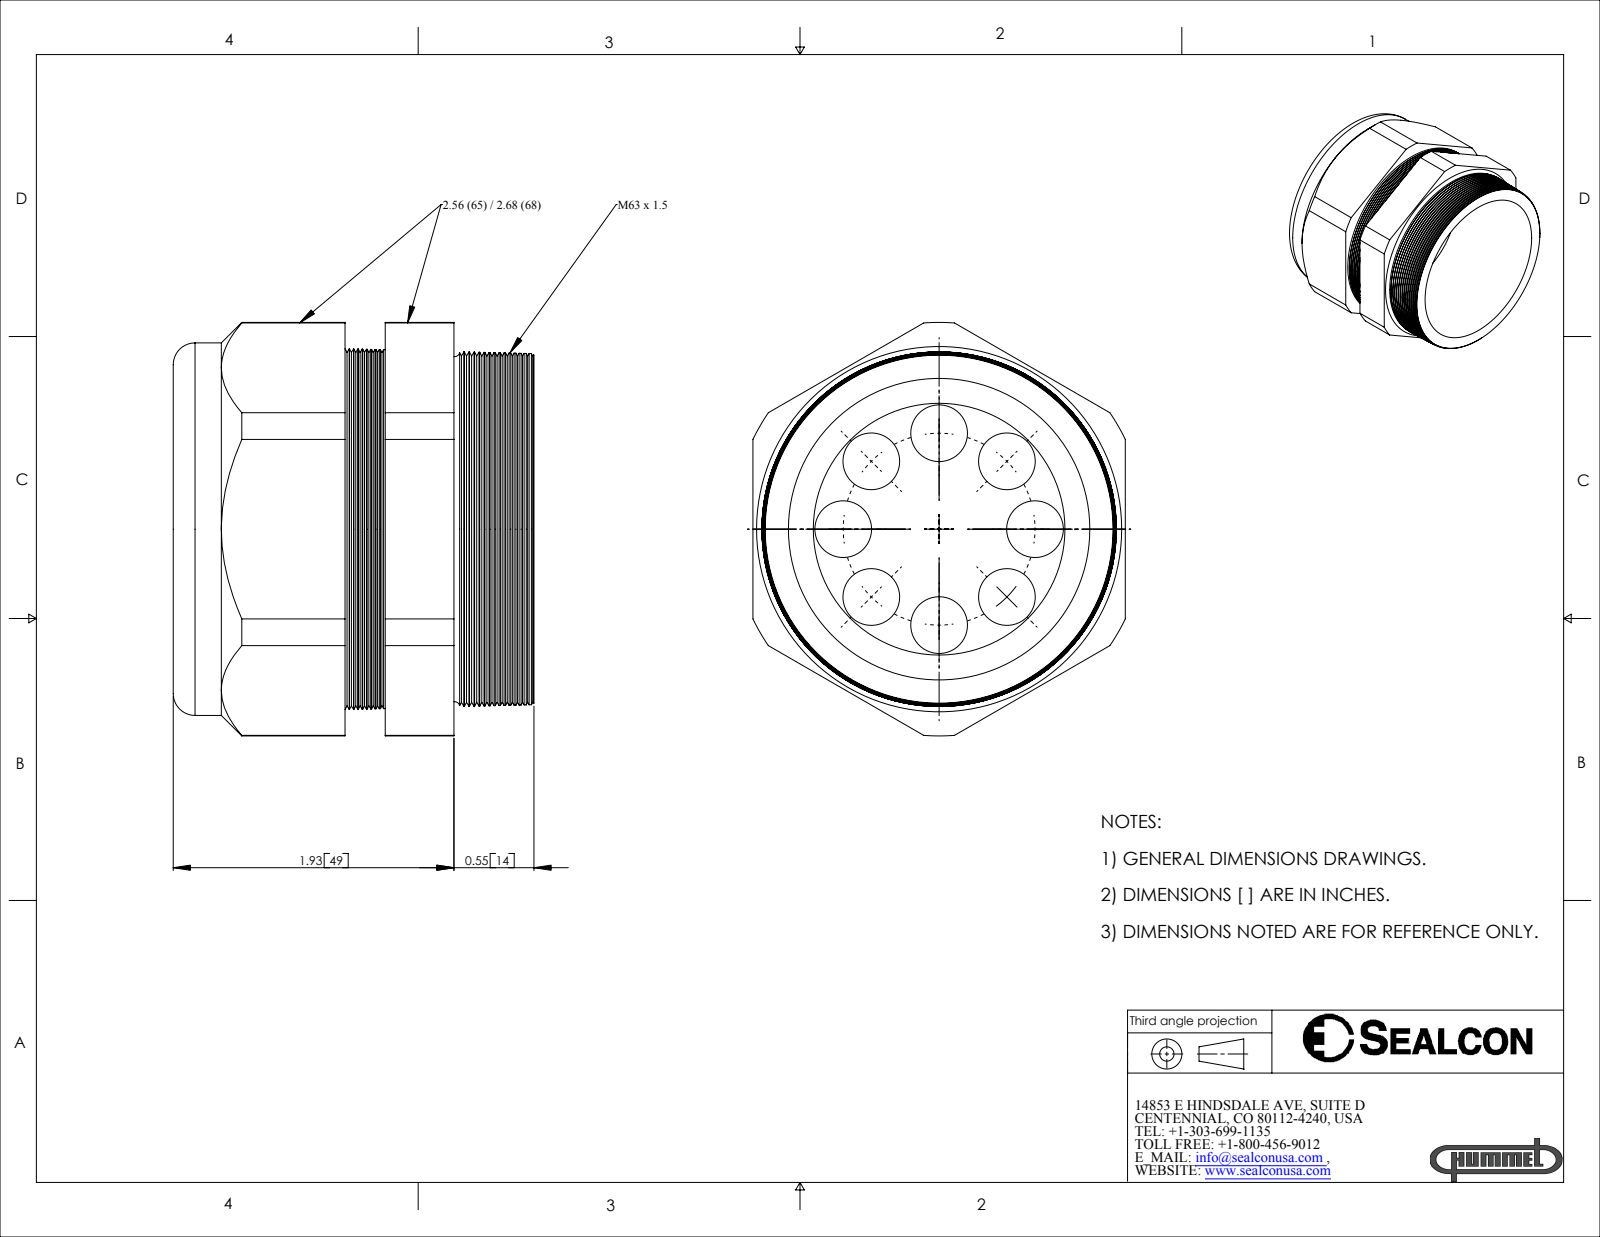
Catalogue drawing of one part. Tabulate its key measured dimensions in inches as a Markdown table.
| quantity | value |
| --- | --- |
| part name | CD63M1-BK |
| STEP written by | SolidWorks 2007 (CONFIG_CONTROL_DESIGN) |
| units | inches |
| bodies | 2 solids, 214 faces (20 planar, 36 cylindrical, 158 other) |
| overall size | 2.842 × 2.56 × 2.48 |
| volume | 7.094 in³ |
| surface area | 56.43 in² |
| round holes (diameter × count) | 0.39 × 8, 1.71 × 1, 1.73 × 1 |
| round bosses / shafts (diameter × count) | 2.56 × 1 |
| partial cylindrical surfaces (radius × count) | 1.421 × 1 |
| main face-to-face distances | 2.56, 0.5, 0.02, 0.48, 2.48, 2.46, 1.98, 1.458, 1.438, 0.958 |
| hole center spacings | 0.504, 0.659, 1.218, 0.932, 0.932, 1.318, 1.319 |
